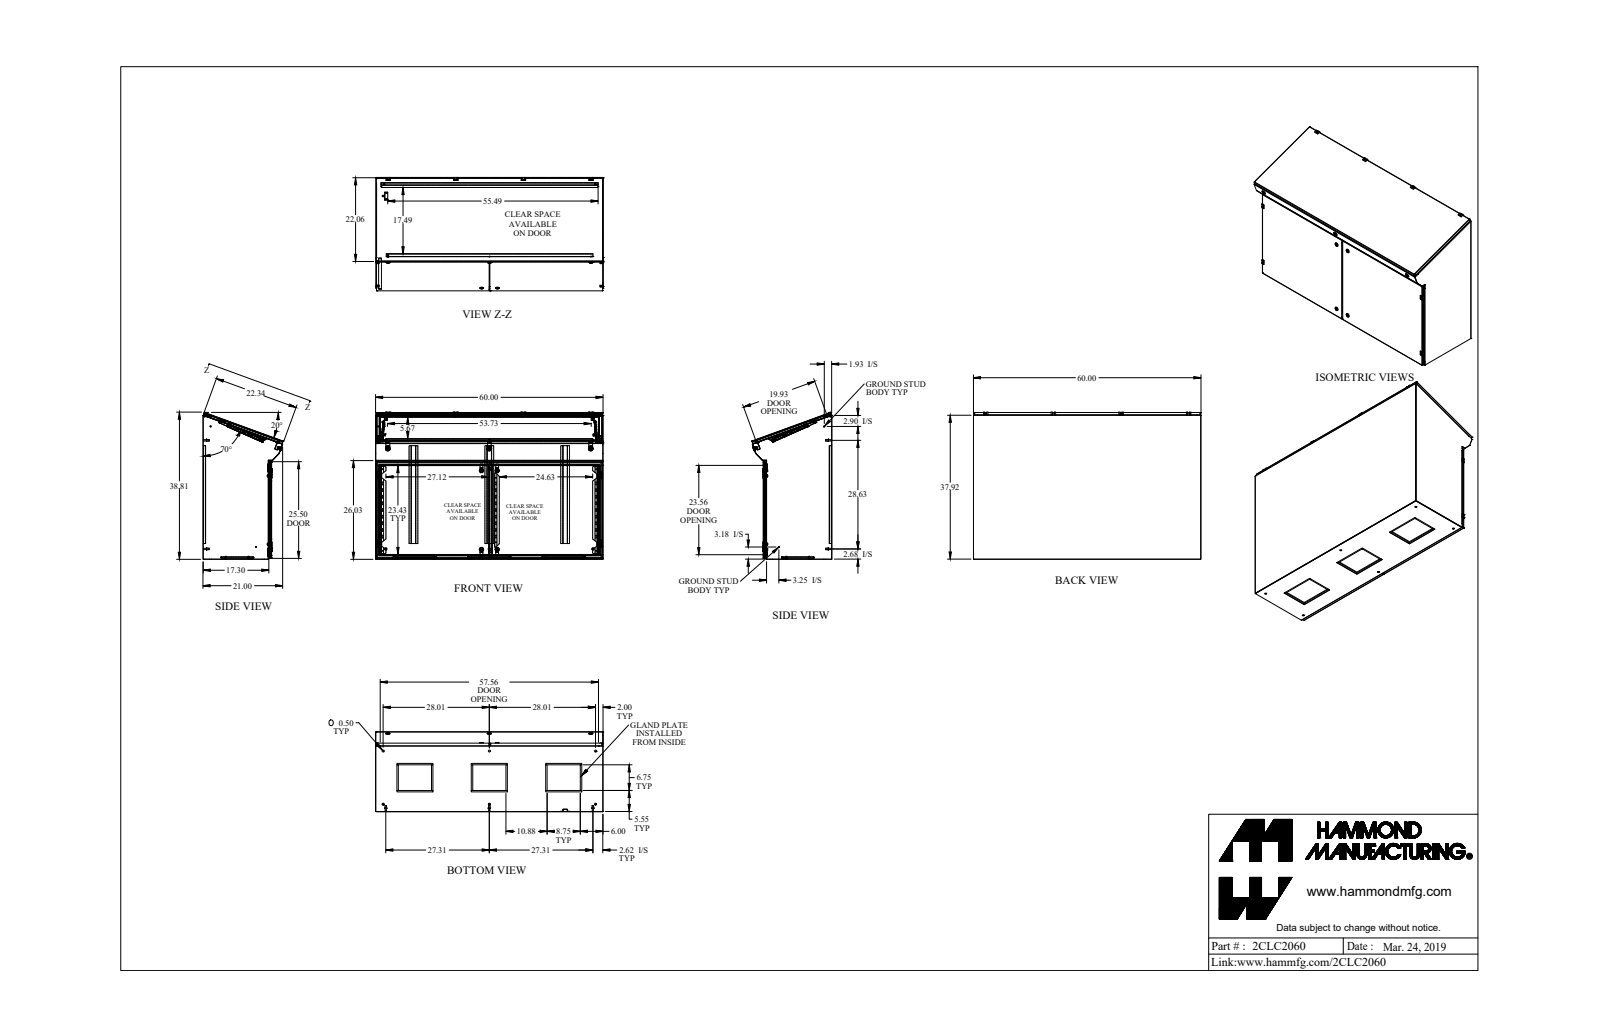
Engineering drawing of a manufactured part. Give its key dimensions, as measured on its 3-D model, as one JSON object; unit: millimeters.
{"part_name": "2CLC2060", "step_written_by": "SolidWorks 2018 (AUTOMOTIVE_DESIGN)", "units": "millimeters", "bodies": {"solids": 173, "faces": 2985, "planar": 2136, "cylindrical": 696, "other": 153}, "overall_size": [1525.4, 988.8, 536], "volume_mm3": 12380000, "surface_area_mm2": 12610000, "round_holes": [[7.1, 68], [5, 13], [12.7, 10], [4.8, 8], [5, 8], [8, 8], [5, 7], [6.4, 4], [7, 4], [7, 4], [9.8, 4], [9.9, 4]], "round_bosses_or_shafts": [[6, 19], [6.4, 17], [7.1, 14], [15.9, 12], [12.7, 8], [5.7, 8], [16.5, 6], [13.3, 6]], "partial_cylinders_radius": [[0.9, 60], [2.7, 60], [3.2, 40], [1.1, 12], [2.9, 12], [4.8, 12], [6.4, 12], [1.2, 8]], "face_to_face_distances": [1.8, 457.5, 457.3, 455.7, 455.4, 1.8, 1.6, 2.1, 459.1, 459.3], "hole_center_spacings": [679.5, 88.9, 44.5, 1358.9, 133.4, 177.8, 266.7, 101.6]}
